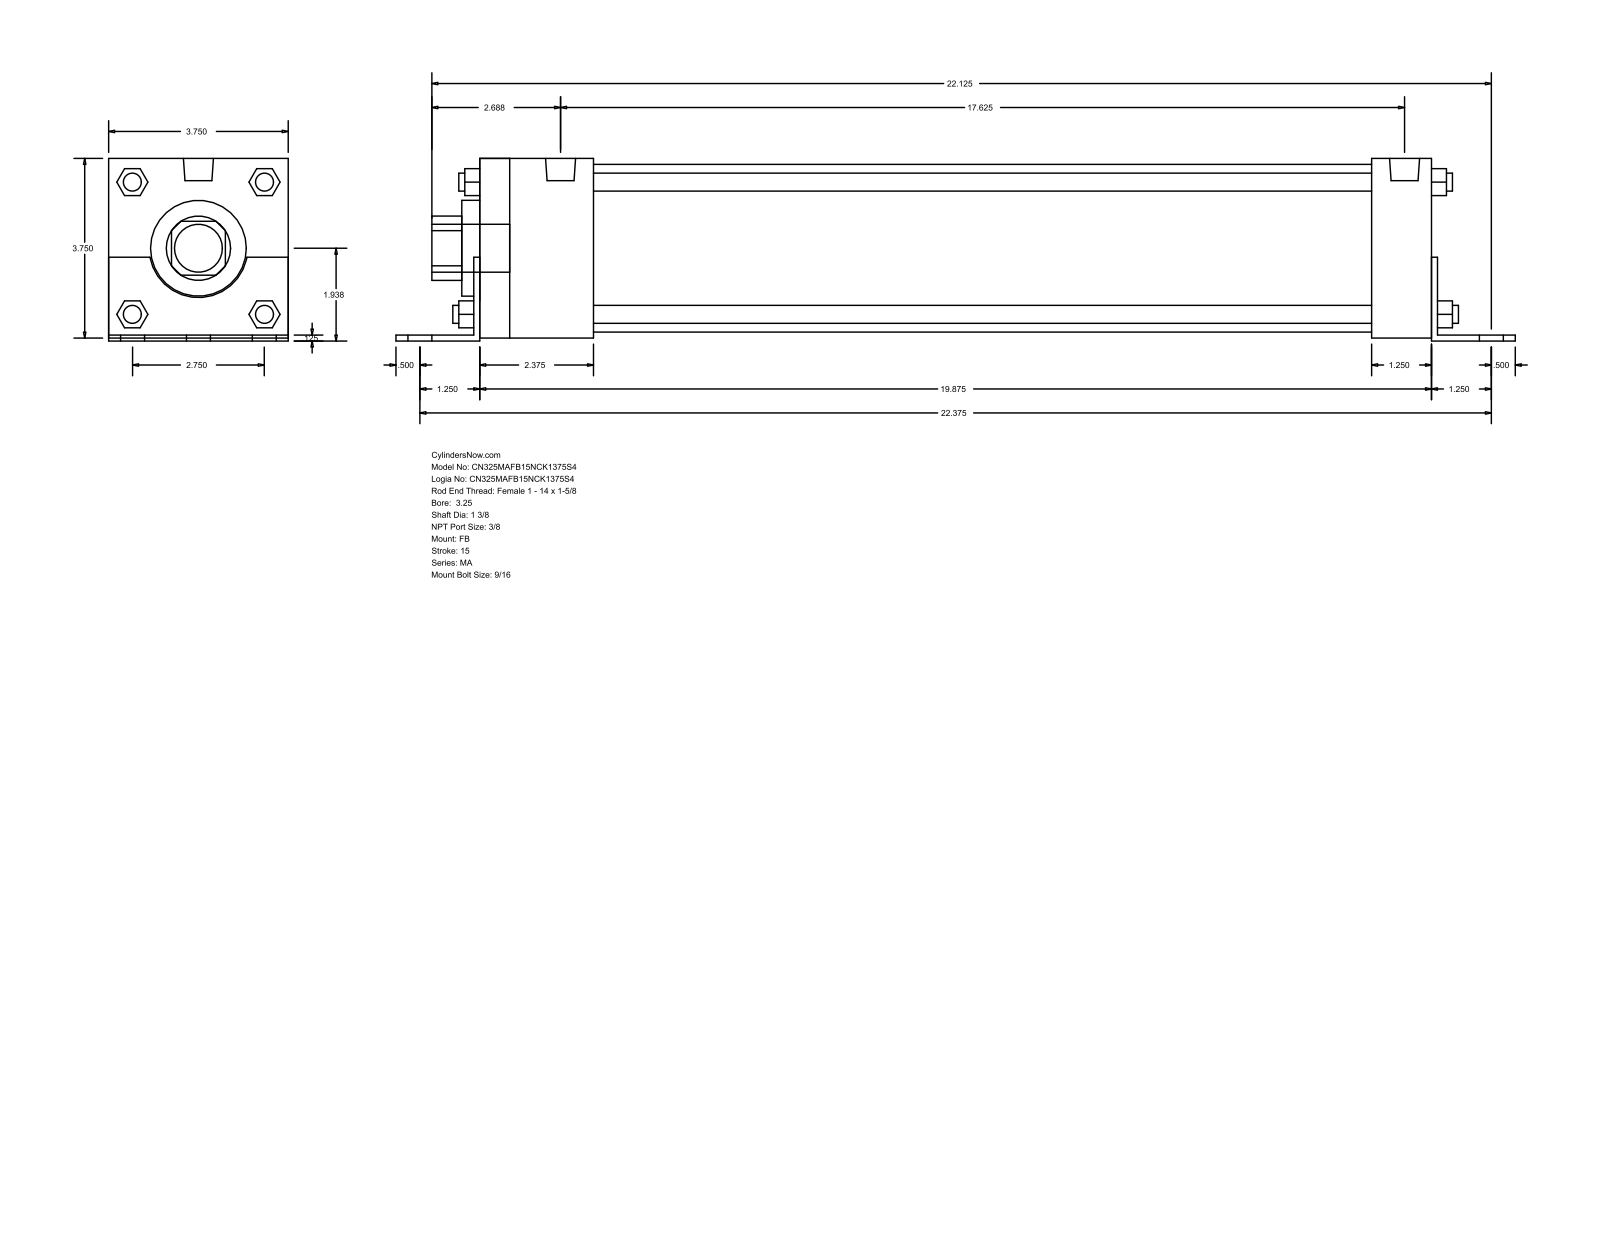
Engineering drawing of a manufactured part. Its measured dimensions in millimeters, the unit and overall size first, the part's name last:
Units: millimetres
Overall size (bounding box): 593.73 × 96.84 × 95.25
Round holes (diameter × count): ⌀34.92 ×1, ⌀50.8 ×1, ⌀88.9 ×1
Round bosses / shafts (diameter × count): ⌀14.29 ×6, ⌀11.11 ×4, ⌀9.53 ×4, ⌀15.93 ×2, ⌀25.4 ×1
Partial cylindrical surfaces — rounded edges, fillets, slot ends (radius × count): R17.06 ×1, R26.16 ×1
Main face-to-face distances: 95.24, 3.17, 1.59, 96.83, 1.58, 93.66, 508, 504.83, 31.75, 60.32
Bodies: 0 solids, 140 faces (105 planar, 35 cylindrical, 0 other)
Part name (STEP PRODUCT): MA_FB__0325_1.375
STEP written by: GSSL Pune (CONFIG_CONTROL_DESIGN)
